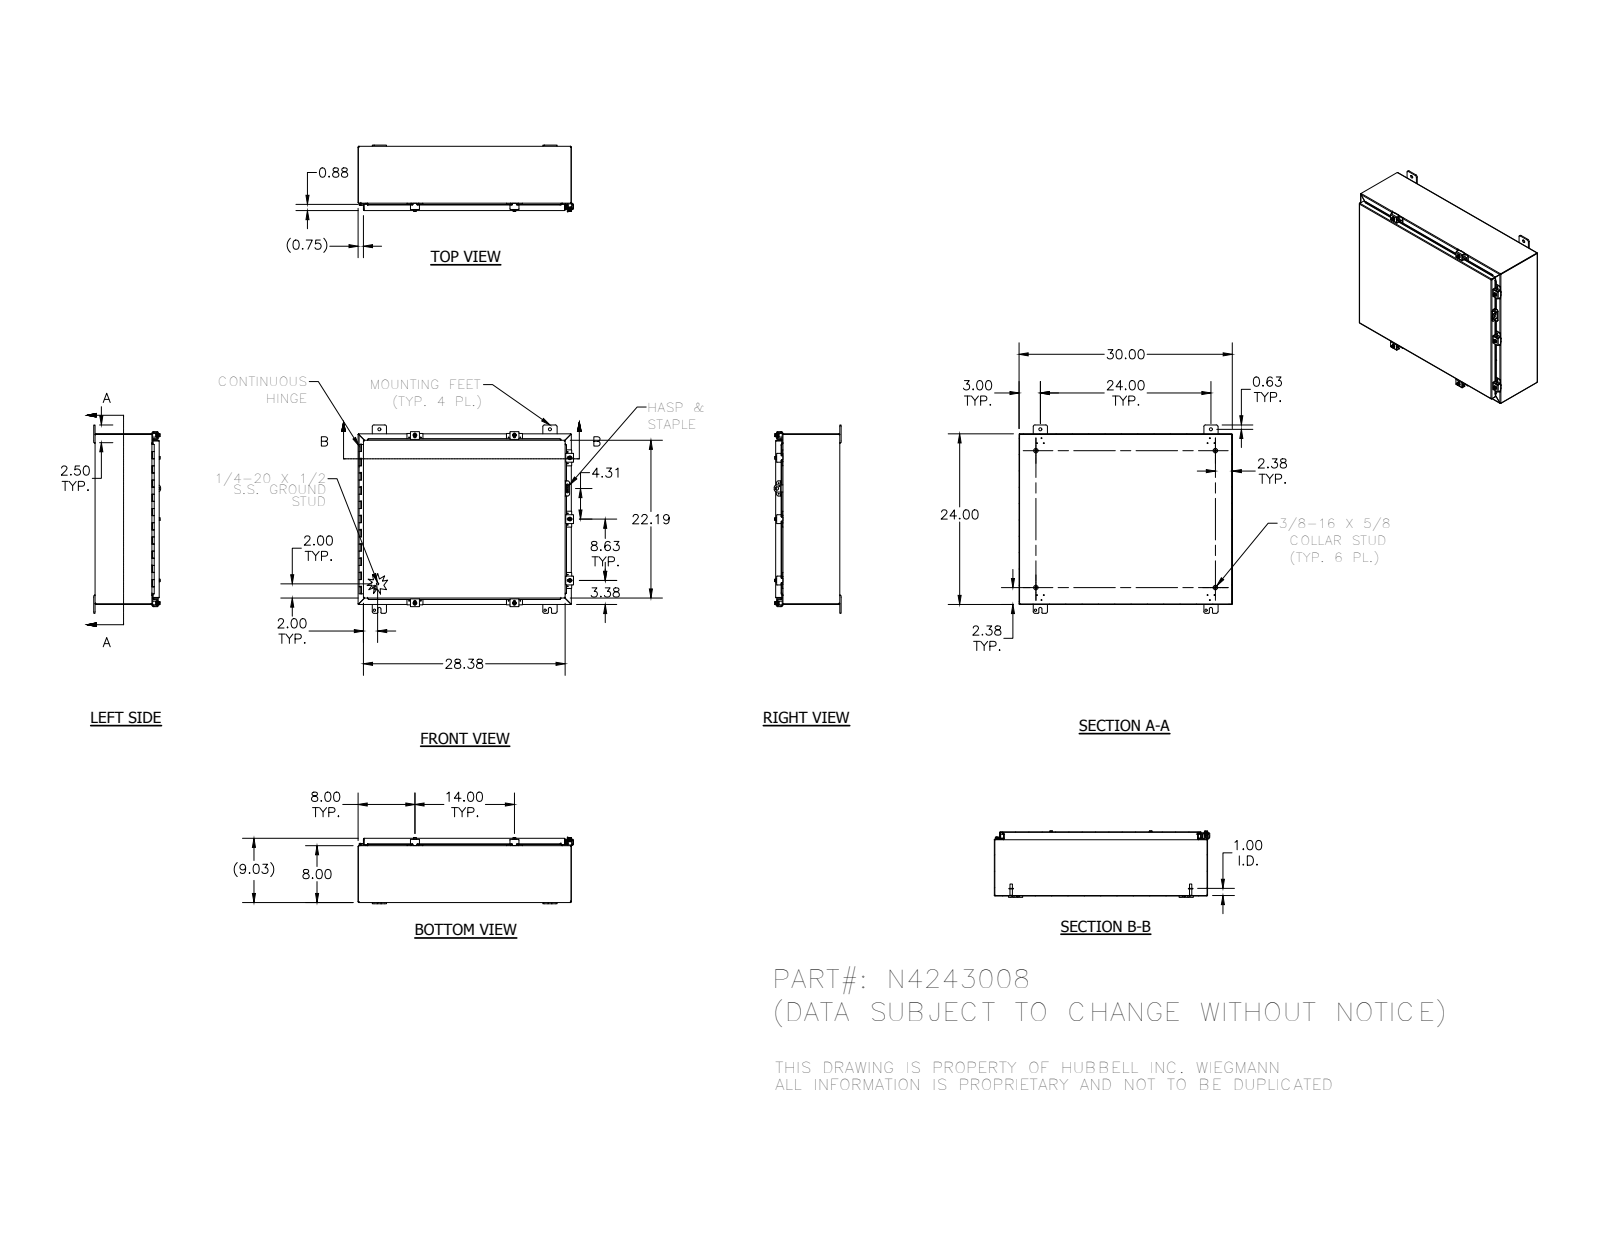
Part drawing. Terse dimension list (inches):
name: 388116_1; 30817_1; 328105L_1; 328105P-1_1 (+8 more)
written by: SolidWorks 2014 (AUTOMOTIVE_DESIGN)
unit: in
bodies: 52 solids, 2242 faces (856 planar, 1003 cylindrical, 383 other)
size: 30.311 × 26.5 × 9.41
volume: 208.1 in³; area: 5 442 in²
holes: 17× ⌀0.11, 12× ⌀0.12, 7× ⌀0.211, 7× ⌀0.281, 7× ⌀0.3, 4× ⌀0.313, 4× ⌀0.438, 1× ⌀0.125, 1× ⌀0.156, 1× ⌀0.5
bosses: 9× ⌀0.25, 7× ⌀0.52, 7× ⌀0.5, 7× ⌀0.35, 4× ⌀0.625, 4× ⌀0.33, 2× ⌀0.115, 1× ⌀0.337
rounds: 83× R0.03, 47× R0.062, 37× R0.125, 33× R0.25, 23× R0.031, 23× R0.105, 14× R0.141, 10× R0.1
face distances: 0.074, 8.959, 8.885, 9.033, 23.926, 29.926, 7.926, 1.033, 23.852, 24
hole spacings: 24, 0.876, 0.759, 0.839, 0.94, 0.969, 1.593, 1.995
